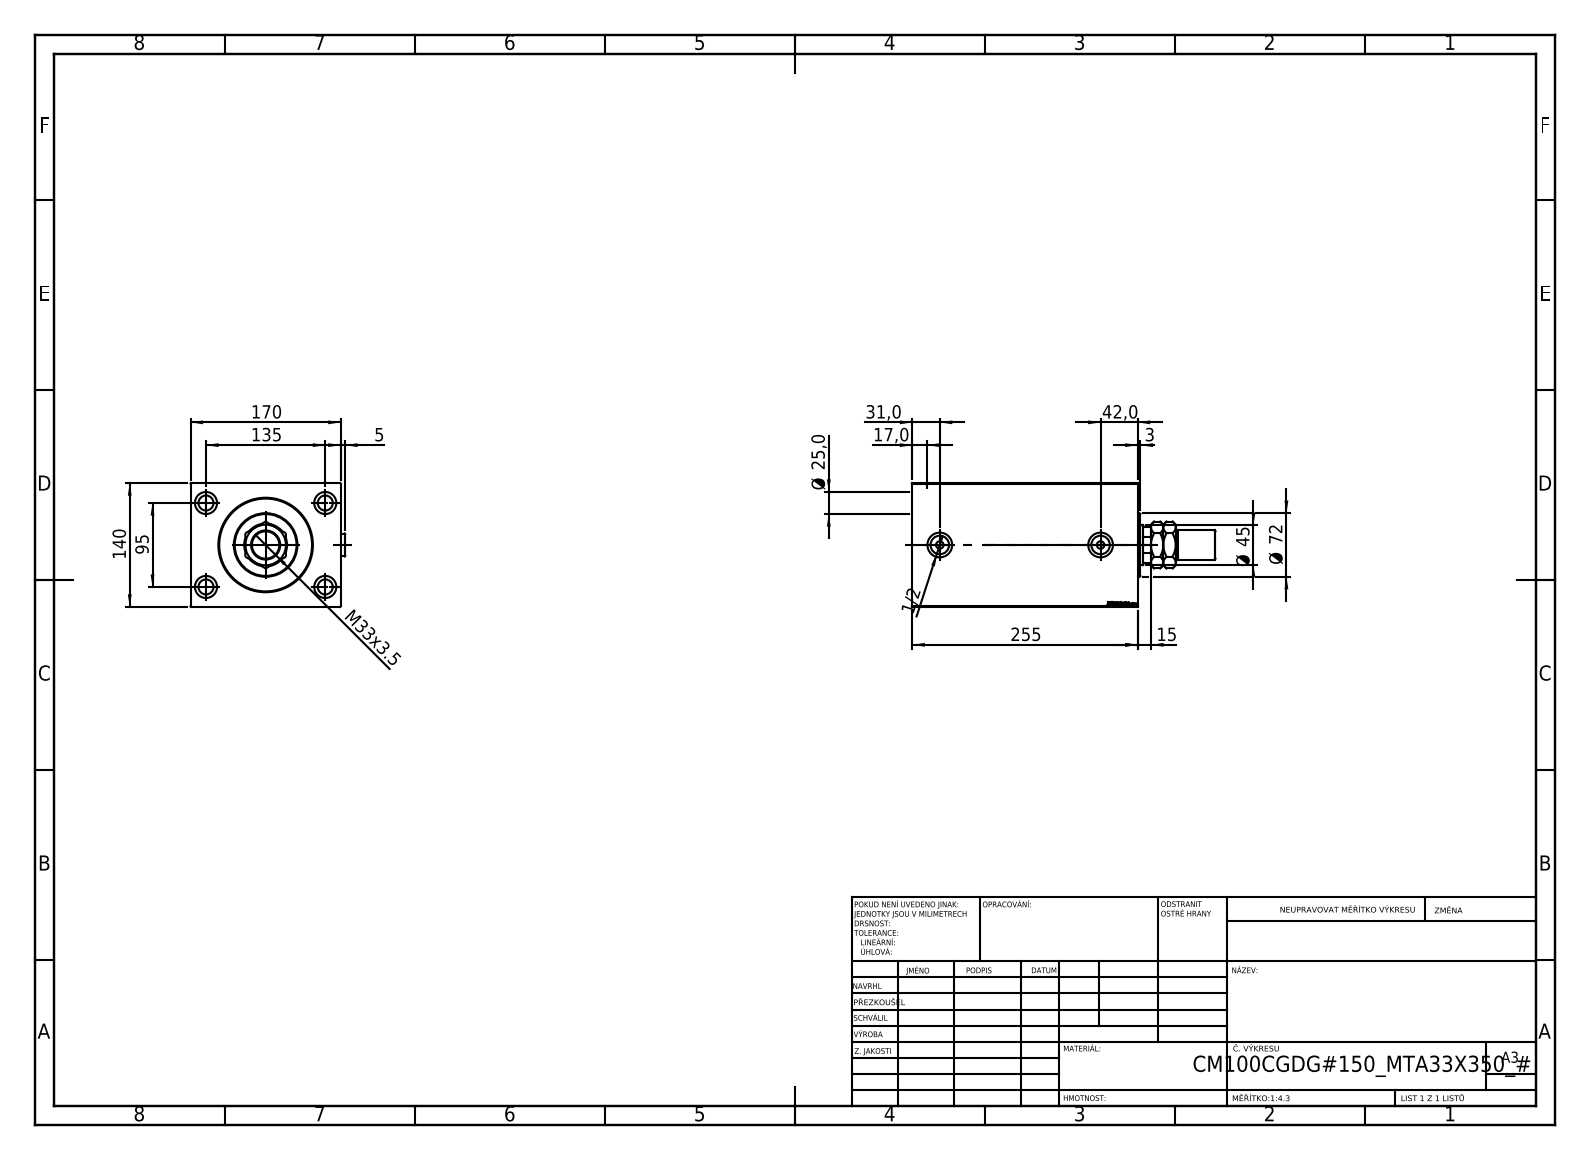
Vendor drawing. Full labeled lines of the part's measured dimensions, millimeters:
Part name (STEP PRODUCT): MTA; V450CM_C_VCP; Zatka_OIL_PORT; V450CM_C_Body (+1 more)
STEP written by: SolidWorks 2019 (CONFIG_CONTROL_DESIGN)
Units: millimetres
Bodies: 6 solids, 968 faces (458 planar, 82 cylindrical, 428 other)
Overall size (bounding box): 343 × 174.9 × 140
Volume: 4 929 000 mm³ · Surface area: 441 724 mm²
Round holes (diameter × count): ⌀17 ×4, ⌀25 ×4, ⌀8.5 ×2, ⌀20.96 ×2, ⌀28 ×2, ⌀31.5 ×1, ⌀45 ×1, ⌀48.5 ×1, ⌀100 ×1, ⌀102 ×1, ⌀105 ×1
Round bosses / shafts (diameter × count): ⌀26 ×2, ⌀72 ×1, ⌀33 ×1, ⌀31 ×1
Partial cylindrical surfaces — rounded edges, fillets, slot ends (radius × count): R22 ×1
Main face-to-face distances: 140, 170, 255, 229, 26, 15, 214, 240, 90, 165
Hole centre spacings: 82.54, 95, 135, 165.08, 182
